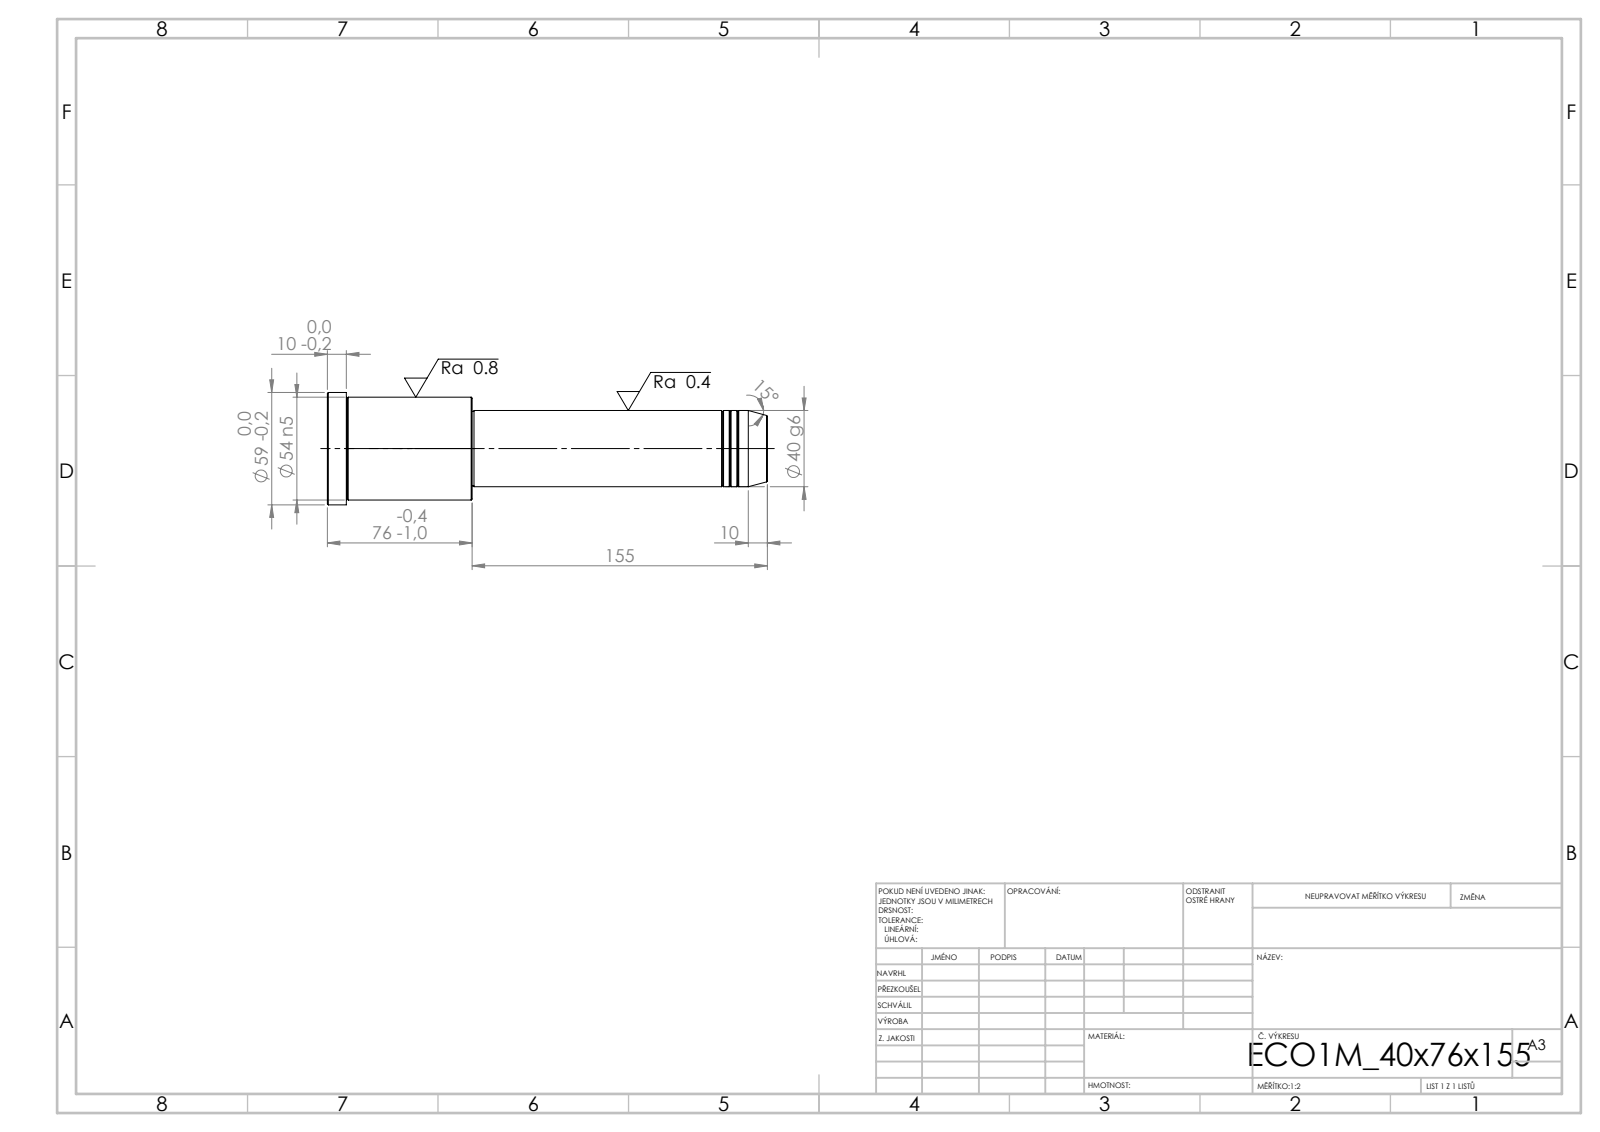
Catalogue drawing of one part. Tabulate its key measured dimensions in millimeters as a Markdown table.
| quantity | value |
| --- | --- |
| STEP written by | SolidWorks 2019 (CONFIG_CONTROL_DESIGN) |
| units | millimeters |
| bodies | 1 solid, 43 faces (5 planar, 14 cylindrical, 24 other) |
| overall size | 231 × 59 × 59 |
| volume | 371 343 mm³ |
| surface area | 37 942 mm² |
| round bosses / shafts (diameter × count) | 59 × 1, 54 × 1, 40 × 1, 39 × 1 |
| main face-to-face distances | 76, 155, 231, 221, 66, 10, 154, 1, 67, 77 |
